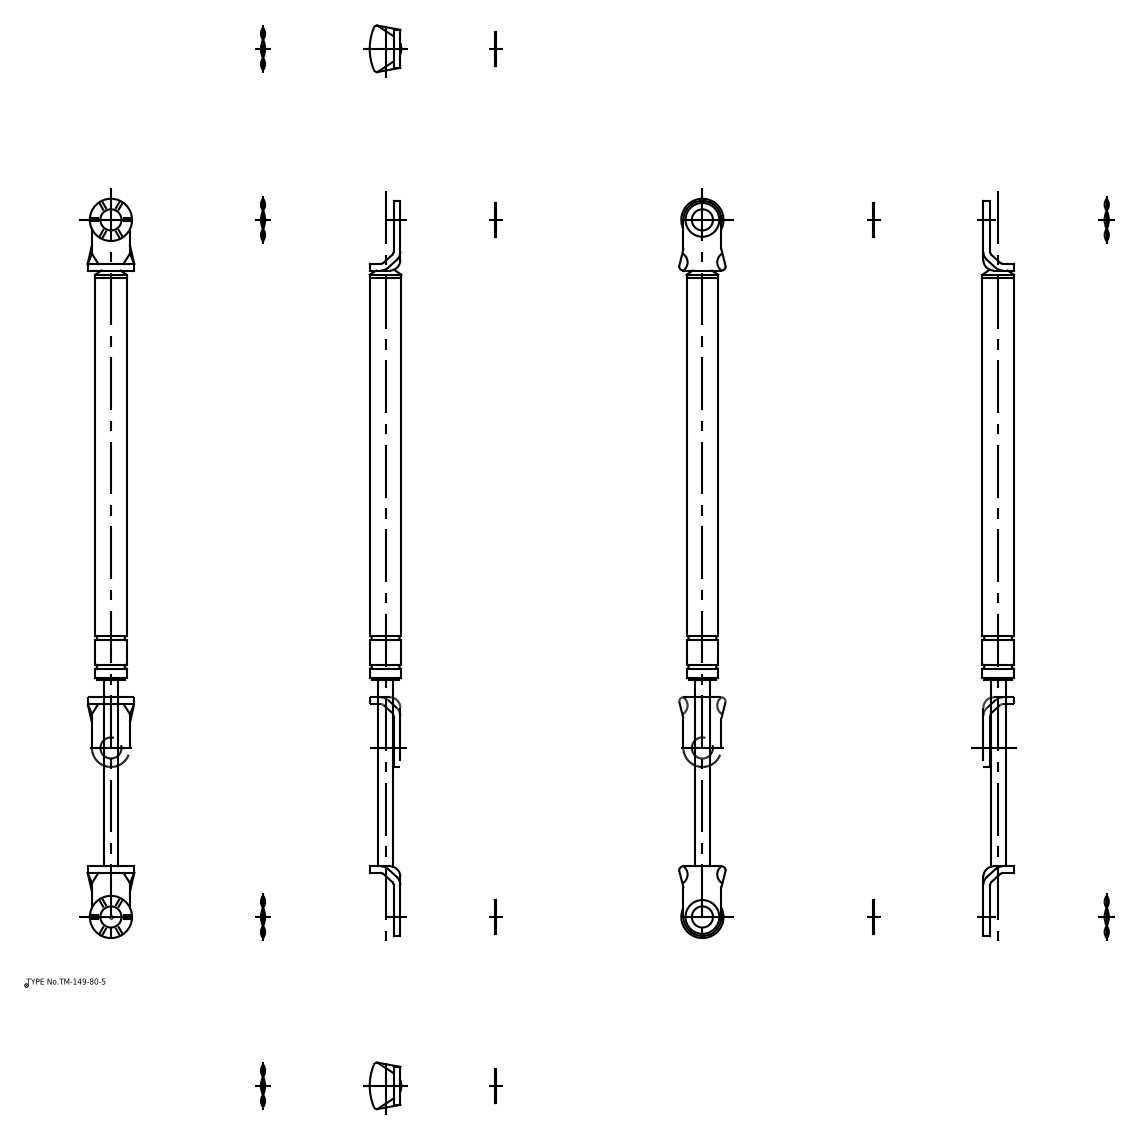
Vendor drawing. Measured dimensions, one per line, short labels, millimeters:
name: washer_2; washer_1; body_div
written by: spGate 16.7.1 (AUTOMOTIVE_DESIGN)
unit: mm
bodies: 6 solids, 92 faces (44 planar, 42 cylindrical, 6 other)
size: 350 × 22 × 15.4
volume: 42 963 mm³; area: 16 956 mm²
holes: 2× ⌀10
bosses: 2× ⌀20, 2× ⌀16, 1× ⌀15.4, 1× ⌀15, 1× ⌀13, 1× ⌀7
rounds: 2× R2, 2× R5, 2× R9, 1× R17.12
face distances: 3.2, 2, 5.2, 285.2, 0.5, 3.7, 5.7, 288.4, 91.2, 197.2
hole spacings: 330
